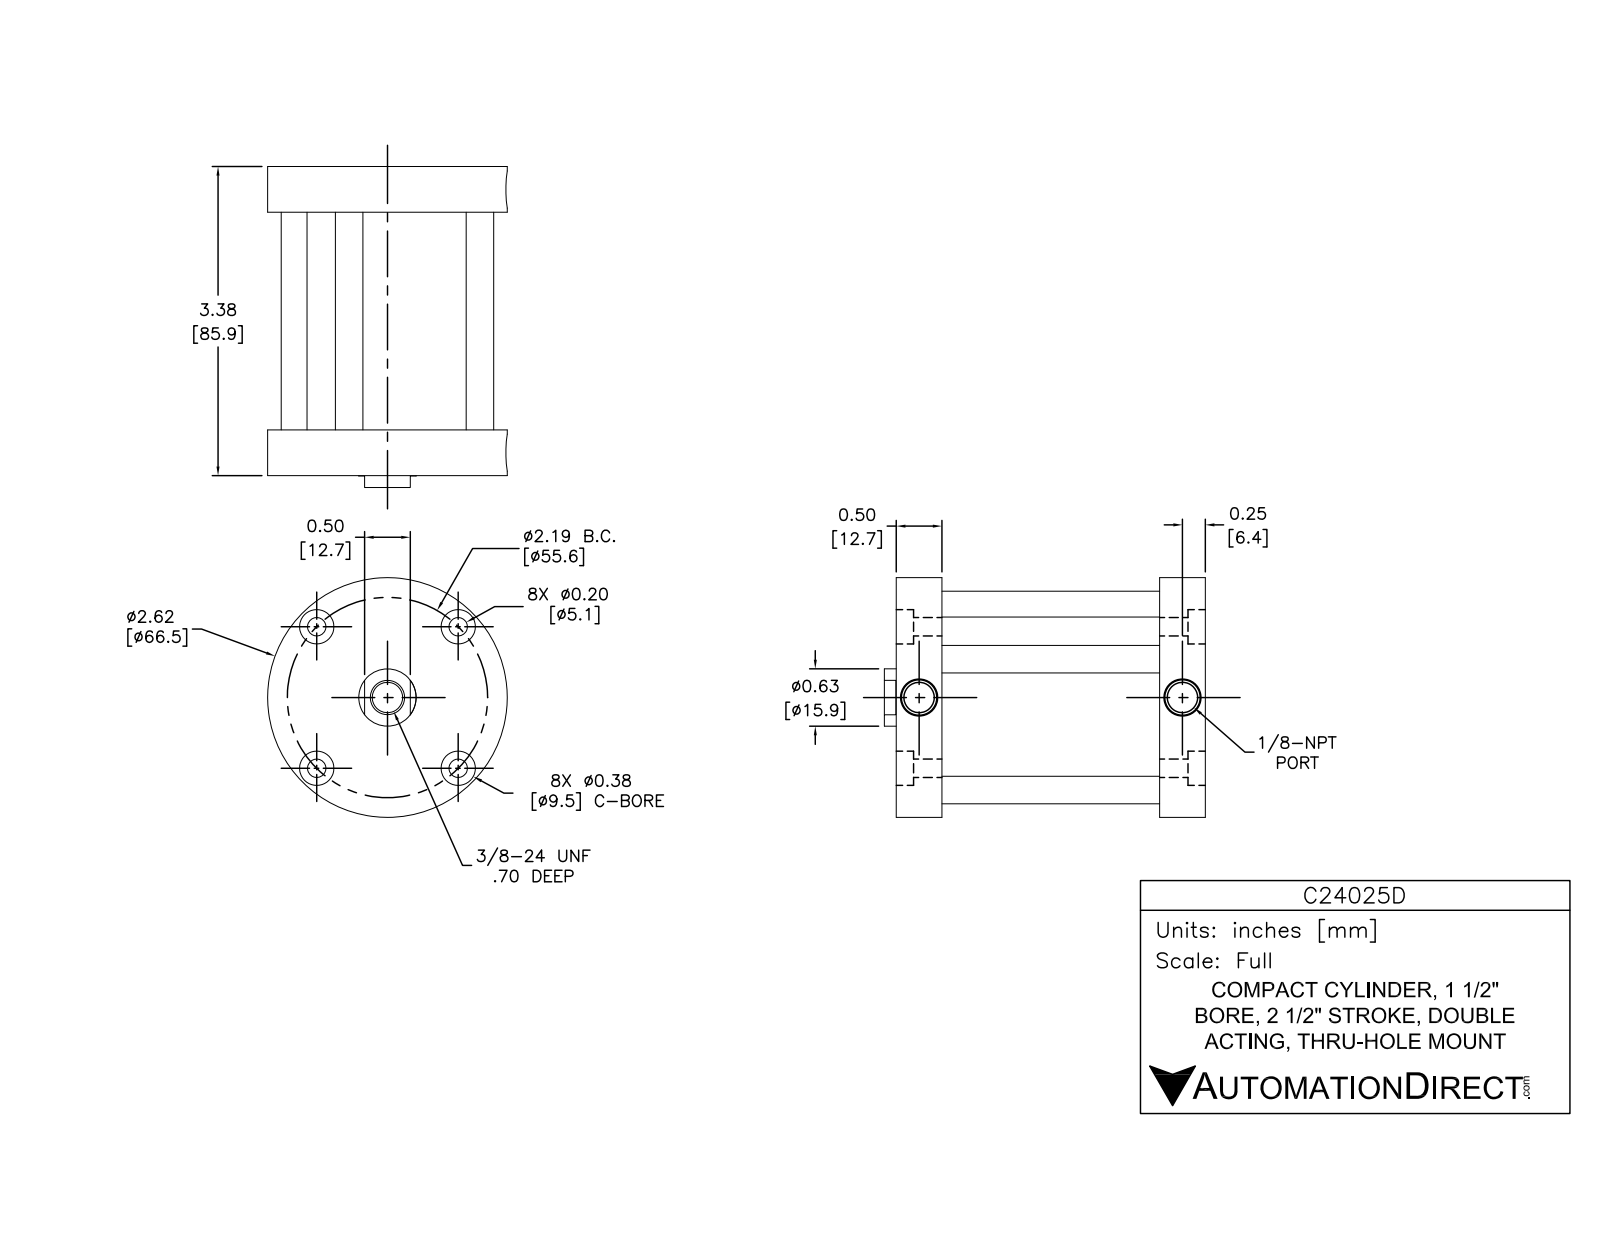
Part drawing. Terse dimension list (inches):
name: C24025D-FO1_BM_heads; C24025D-FO1_BM_tube; C24025D-FO1_BM_heads (2); C24025D-FO1_BM_rod (+3 more)
written by: SolidWorks 2014 (AUTOMOTIVE_DESIGN)
unit: in
bodies: 9 solids, 165 faces (49 planar, 98 cylindrical, 18 other)
size: 3.51 × 2.62 × 2.62
volume: 7.152 in³; area: 90.85 in²
holes: 4× ⌀0.2, 4× ⌀0.218, 4× ⌀0.343, 2× ⌀0.125, 1× ⌀0.33, 1× ⌀0.63, 1× ⌀0.632, 1× ⌀1.503, 1× ⌀1.563
bosses: 4× ⌀0.4, 1× ⌀2.62
face distances: 0.5, 2.88, 0.282, 3.098, 2.598, 0.218, 3.38, 2.38, 2.816, 0.598
hole spacings: 1.095, 1.549, 0.428, 1.217, 1.821, 2.148, 2.19, 2.191
